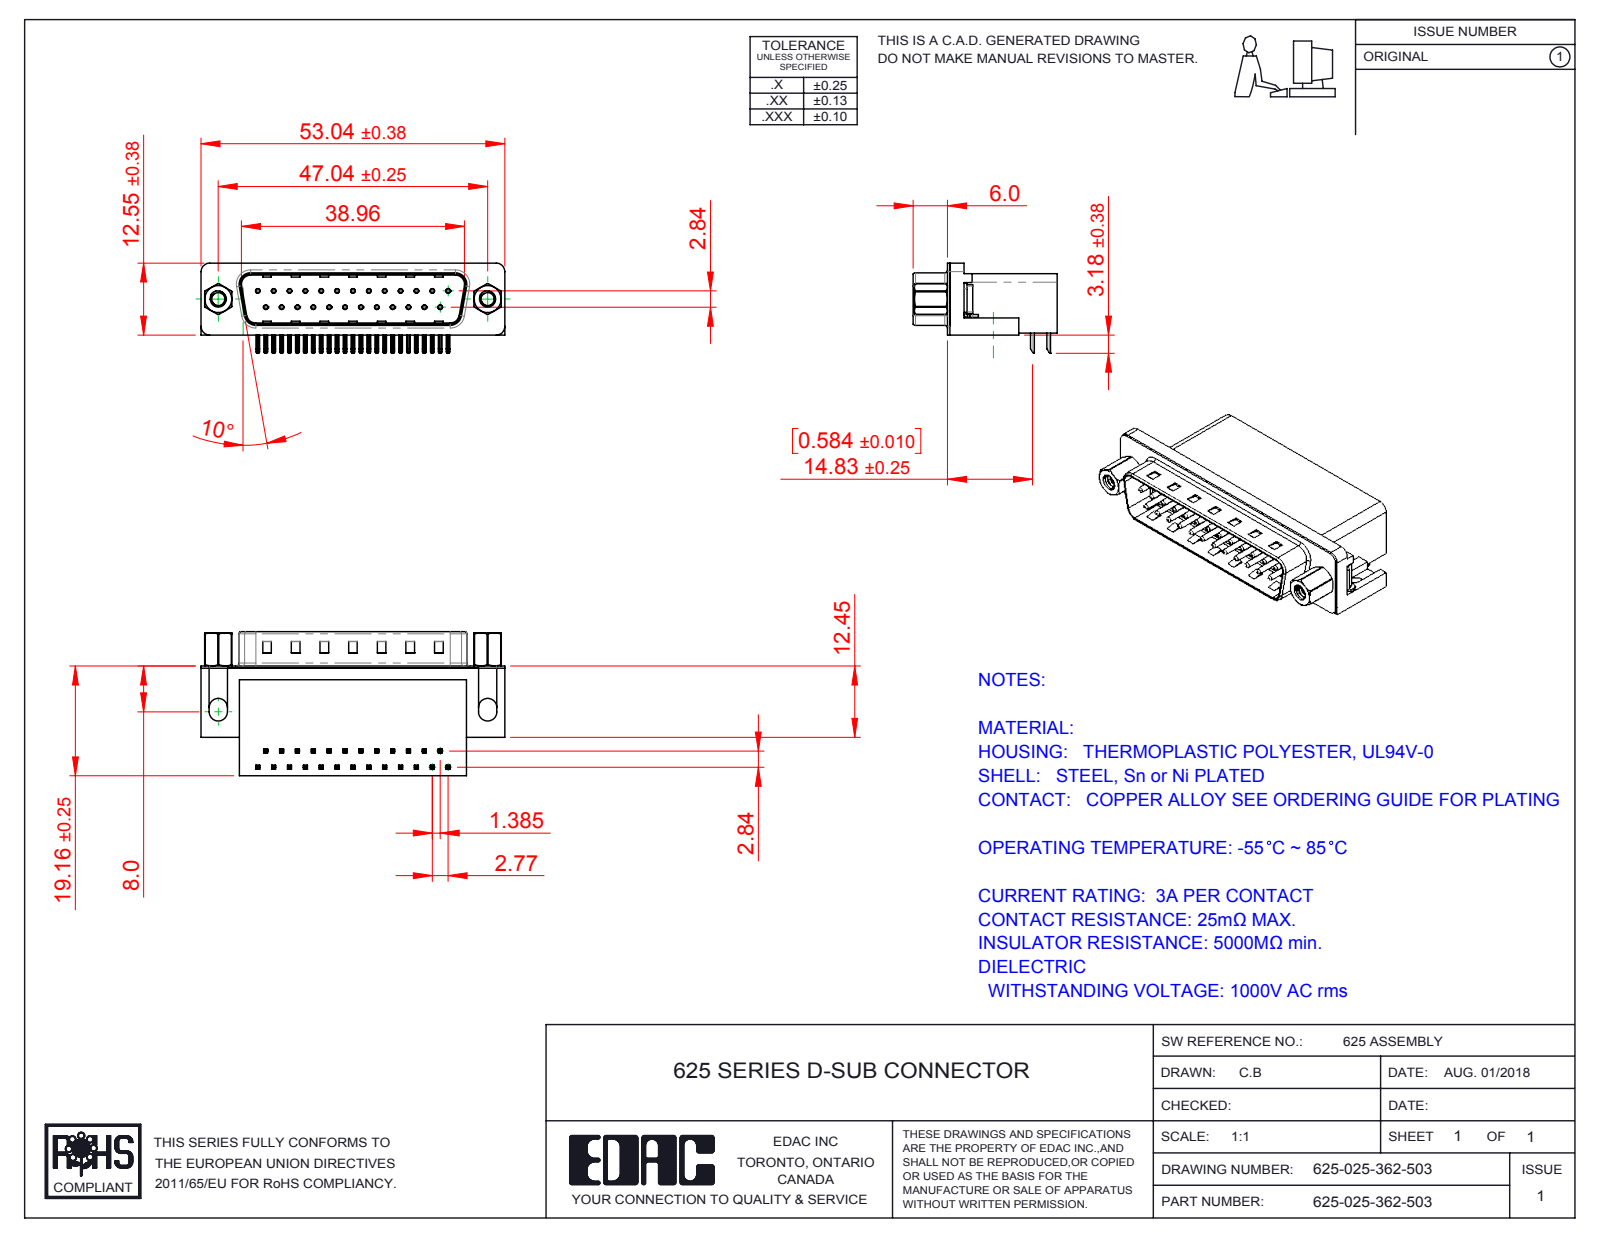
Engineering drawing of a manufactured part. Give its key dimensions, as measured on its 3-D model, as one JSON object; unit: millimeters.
{"part_name": "625 4-40 Hex Standoff 5; 625 4-40 Threaded Rivet; 625 Shell_25 Socket; 625 Contact Bottom (+4 more)", "step_written_by": "SolidWorks 2016 (CONFIG_CONTROL_DESIGN)", "units": "millimeters", "bodies": {"solids": 33, "faces": 2389, "planar": 1429, "cylindrical": 729, "other": 231}, "overall_size": [53.04, 25.16, 15.73], "volume_mm3": 9350, "surface_area_mm2": 9211, "round_holes": [[0.35, 25], [0.8, 25], [2.26, 2], [2.29, 2], [4, 2], [4.8, 2], [5, 2]], "round_bosses_or_shafts": [[0.75, 25], [4.9, 2], [4.75, 2], [3.9, 2], [2.79, 2]], "partial_cylinders_radius": [[0.25, 108], [0.12, 50], [1, 16], [0.5, 9], [1.6, 8], [1.5, 7], [0.9, 4], [2, 4]], "face_to_face_distances": [0.4, 10.35, 18.76, 2.1, 8.76, 10.46, 10.86, 1.7, 19.16, 10.11], "hole_center_spacings": [3.16, 2.77, 11.08, 5.54, 8.31, 5.03, 13.85, 7.48]}
